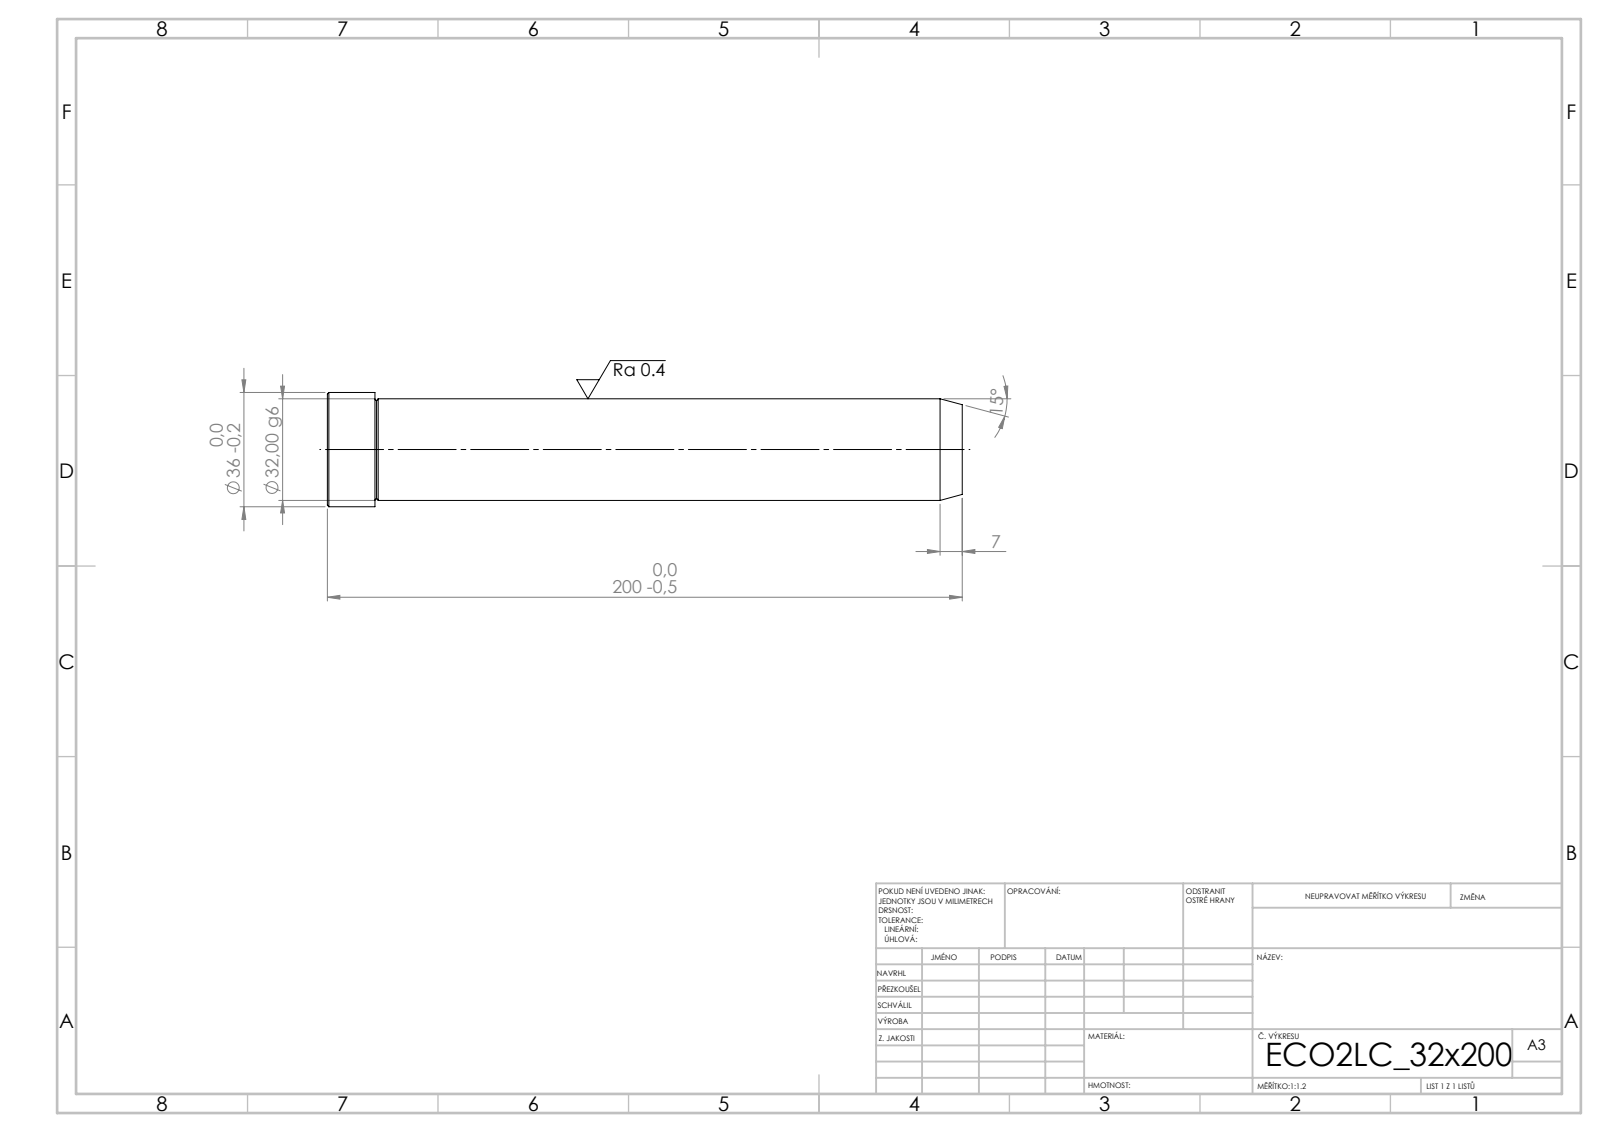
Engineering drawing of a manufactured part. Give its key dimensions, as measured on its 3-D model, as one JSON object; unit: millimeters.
{"step_written_by": "SolidWorks 2019 (CONFIG_CONTROL_DESIGN)", "units": "millimeters", "bodies": {"solids": 1, "faces": 15, "planar": 3, "cylindrical": 4, "other": 8}, "overall_size": [200, 36, 36], "volume_mm3": 163367, "surface_area_mm2": 22156, "round_bosses_or_shafts": [[36, 1], [32, 1]], "face_to_face_distances": [200, 185, 15]}
